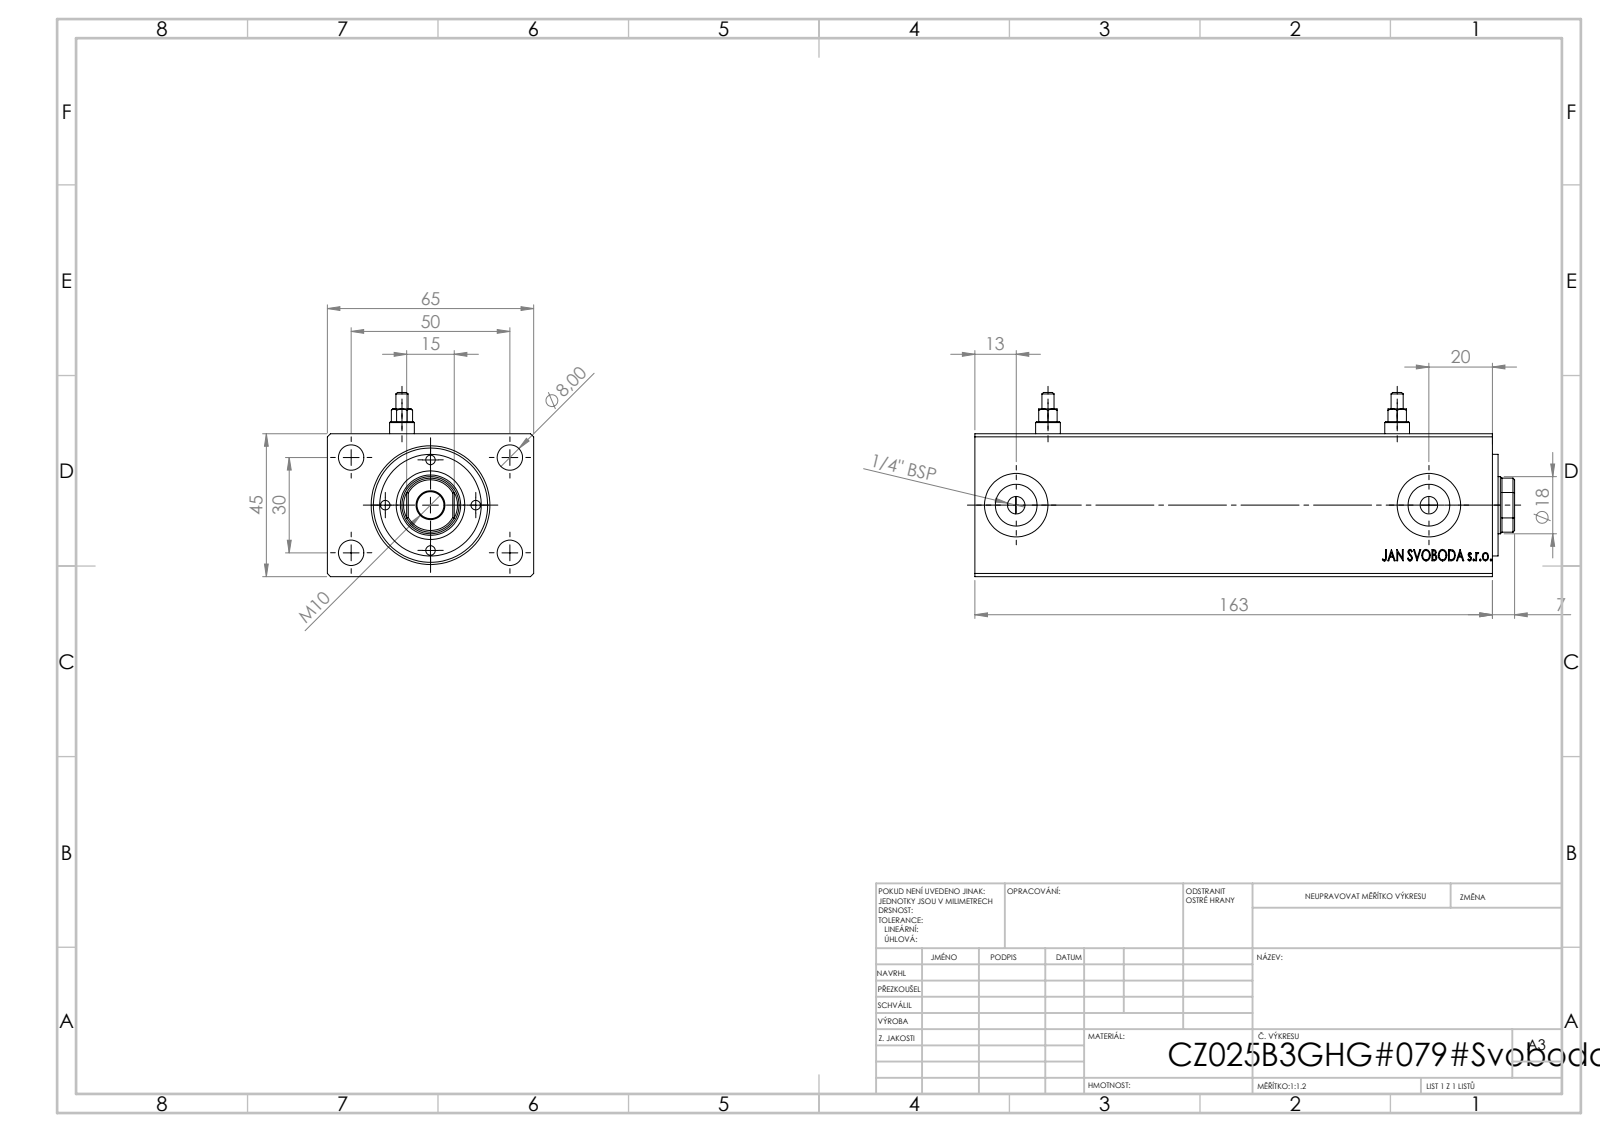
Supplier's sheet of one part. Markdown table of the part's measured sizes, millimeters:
| quantity | value |
| --- | --- |
| part name | V500CZ; V500CZ_B_VC; Zatka_Cushioning3 |
| STEP written by | SolidWorks 2019 (CONFIG_CONTROL_DESIGN) |
| units | millimeters |
| bodies | 5 solids, 933 faces (423 planar, 74 cylindrical, 436 other) |
| overall size | 170 × 65 × 58 |
| volume | 444 175 mm³ |
| surface area | 74 862 mm² |
| round holes (diameter × count) | 8 × 6, 3 × 4, 1.8 × 2, 5.5 × 2, 13.16 × 2, 20 × 2, 8.5 × 1, 18 × 1, 19 × 1, 25 × 1, 36 × 1 |
| round bosses / shafts (diameter × count) | 7.8 × 2, 3.8 × 2, 32 × 1 |
| partial cylindrical surfaces (radius × count) | 8.5 × 1 |
| main face-to-face distances | 45, 65, 163, 7, 162.8, 12.8, 150.2, 12.6, 1.8, 5.2 |
| hole center spacings | 14.25, 18.45, 20.15, 25.01, 29.15, 38.48, 42.02, 28.5 |
